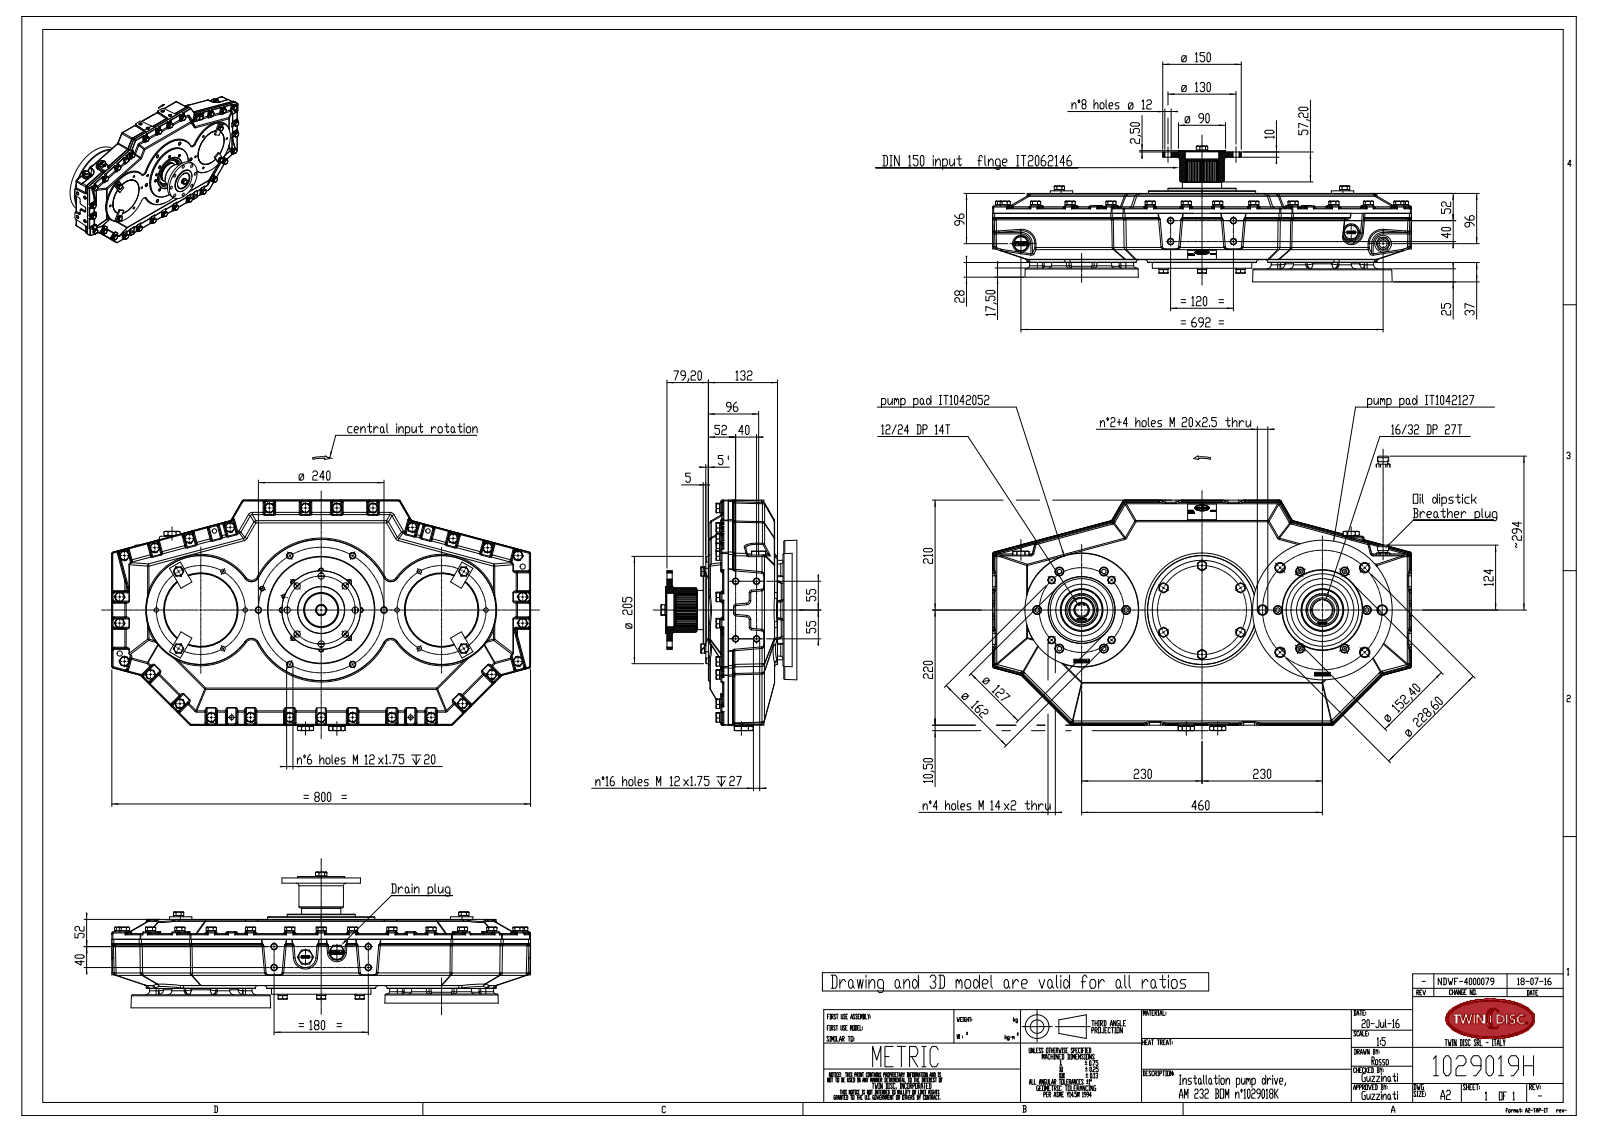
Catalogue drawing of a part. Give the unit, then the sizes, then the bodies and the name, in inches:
Units: inches
Overall size (bounding box): 31.496 × 20.671 × 10.217
Round holes (diameter × count): ⌀0.402 ×58, ⌀0.335 ×30, ⌀0.472 ×30, ⌀0.413 ×29, ⌀0.433 ×18, ⌀0.669 ×12, ⌀0.394 ×10, ⌀0.689 ×6, ⌀0.551 ×4, ⌀0.728 ×3, ⌀1.26 ×3, ⌀3.15 ×3
Round bosses / shafts (diameter × count): ⌀0.394 ×47, ⌀0.713 ×39, ⌀0.638 ×39, ⌀0.63 ×12, ⌀0.787 ×7, ⌀5.512 ×3, ⌀3.886 ×3, ⌀3.228 ×3
Partial cylindrical surfaces — rounded edges, fillets, slot ends (radius × count): R0.079 ×284, R0.197 ×112, R0.118 ×92, R0.098 ×76, R0.018 ×58, R0.059 ×12, R0.315 ×12, R0.394 ×6
Main face-to-face distances: 4.98, 5.197, 1.496, 3.701, 0.65, 0.118, 0.217, 3.484, 5.551, 1.673
Hole centre spacings: 4.724, 2.26, 2.953, 5.456, 1.575, 5.906, 8.183, 1.181
Volume: 278.5 in³ · Surface area: 4 442 in²
Bodies: 39 solids, 6620 faces (2762 planar, 1811 cylindrical, 2047 other)
Part name (STEP PRODUCT): IT0000394_rev00-installation; ITB00810000_rev01-installation; 1029019H; ITam230-001_rev01-installation (+8 more)
STEP written by: SolidWorks 2019 (AUTOMOTIVE_DESIGN)
